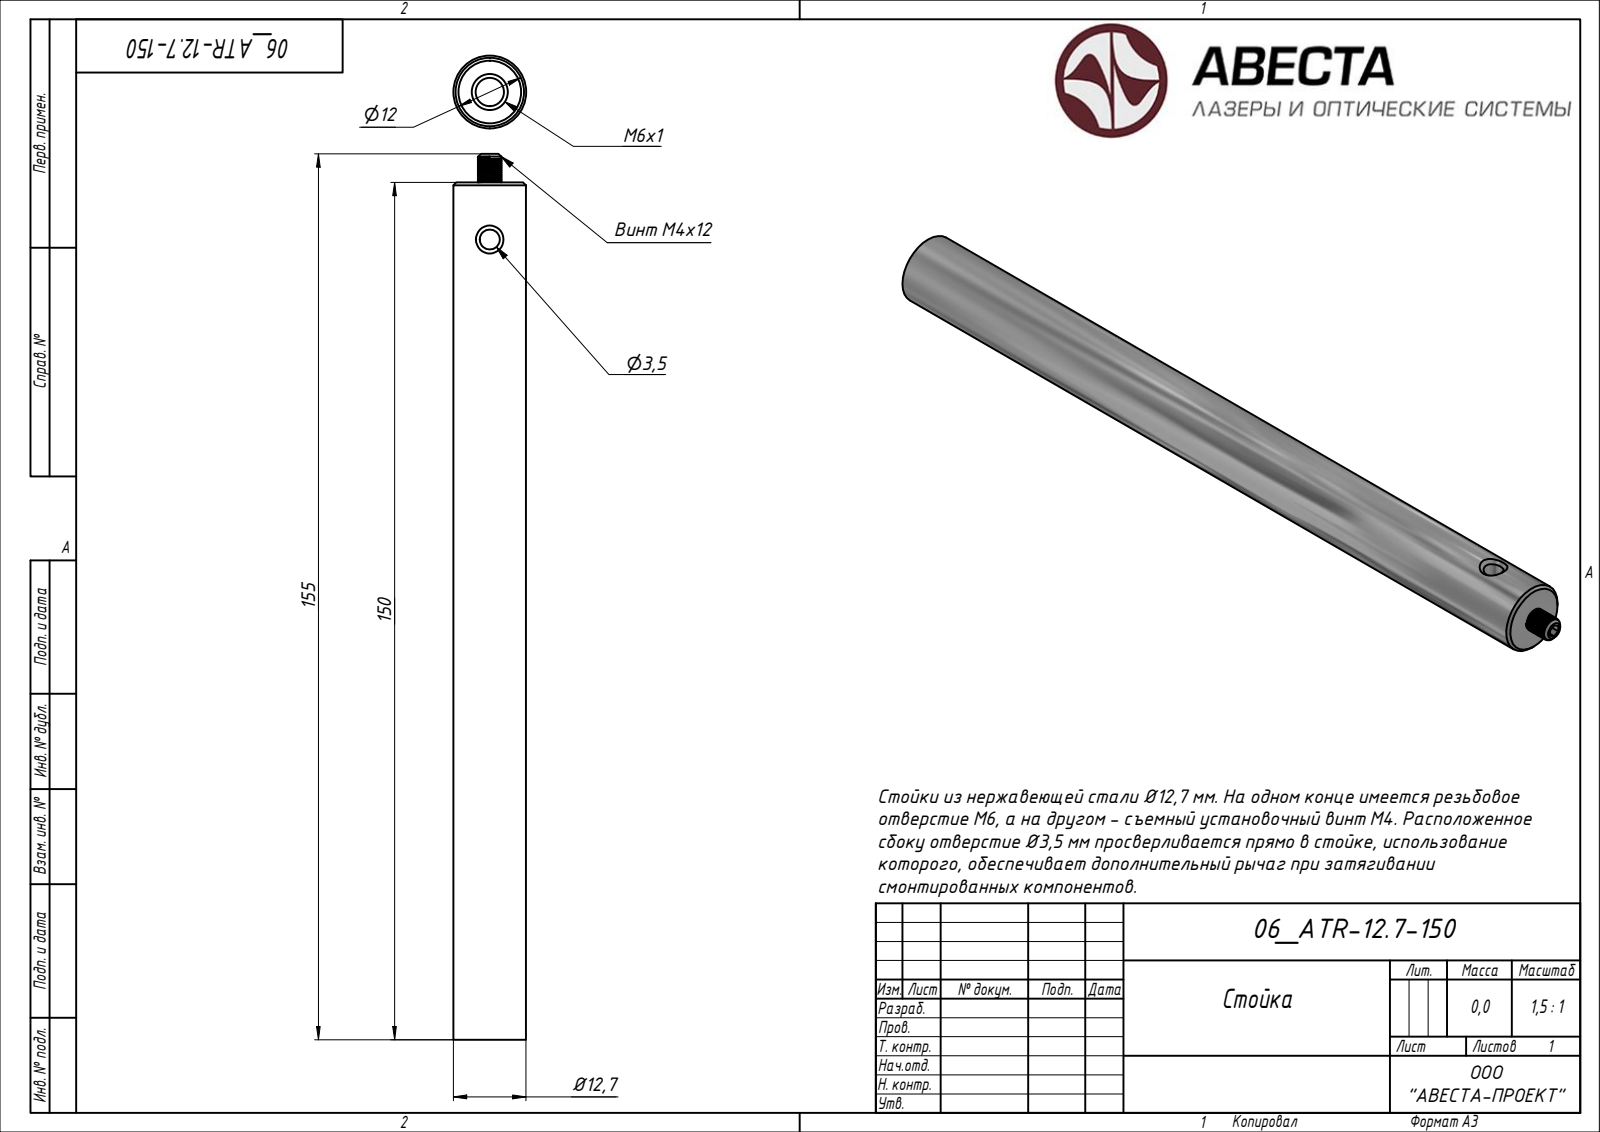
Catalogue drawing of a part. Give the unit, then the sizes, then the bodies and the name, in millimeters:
Units: millimetres
Overall size (bounding box): 155 × 141.25 × 12.7
Main face-to-face distances: 30, 20, 50, 10, 80, 40, 70, 100, 60, 130
Volume: 56 864 mm³ · Surface area: 23 541 mm²
Bodies: 14 solids, 672 faces (98 planar, 0 cylindrical, 574 other)
Part name (STEP PRODUCT): 06_ATR-12.7-1007; 06_ATR-12.7-100; Винт М4х1223456; 06_ATR-12.7-706 (+7 more)
STEP written by: ST-DEVELOPER v15 (AUTOMOTIVE_DESIGN)
